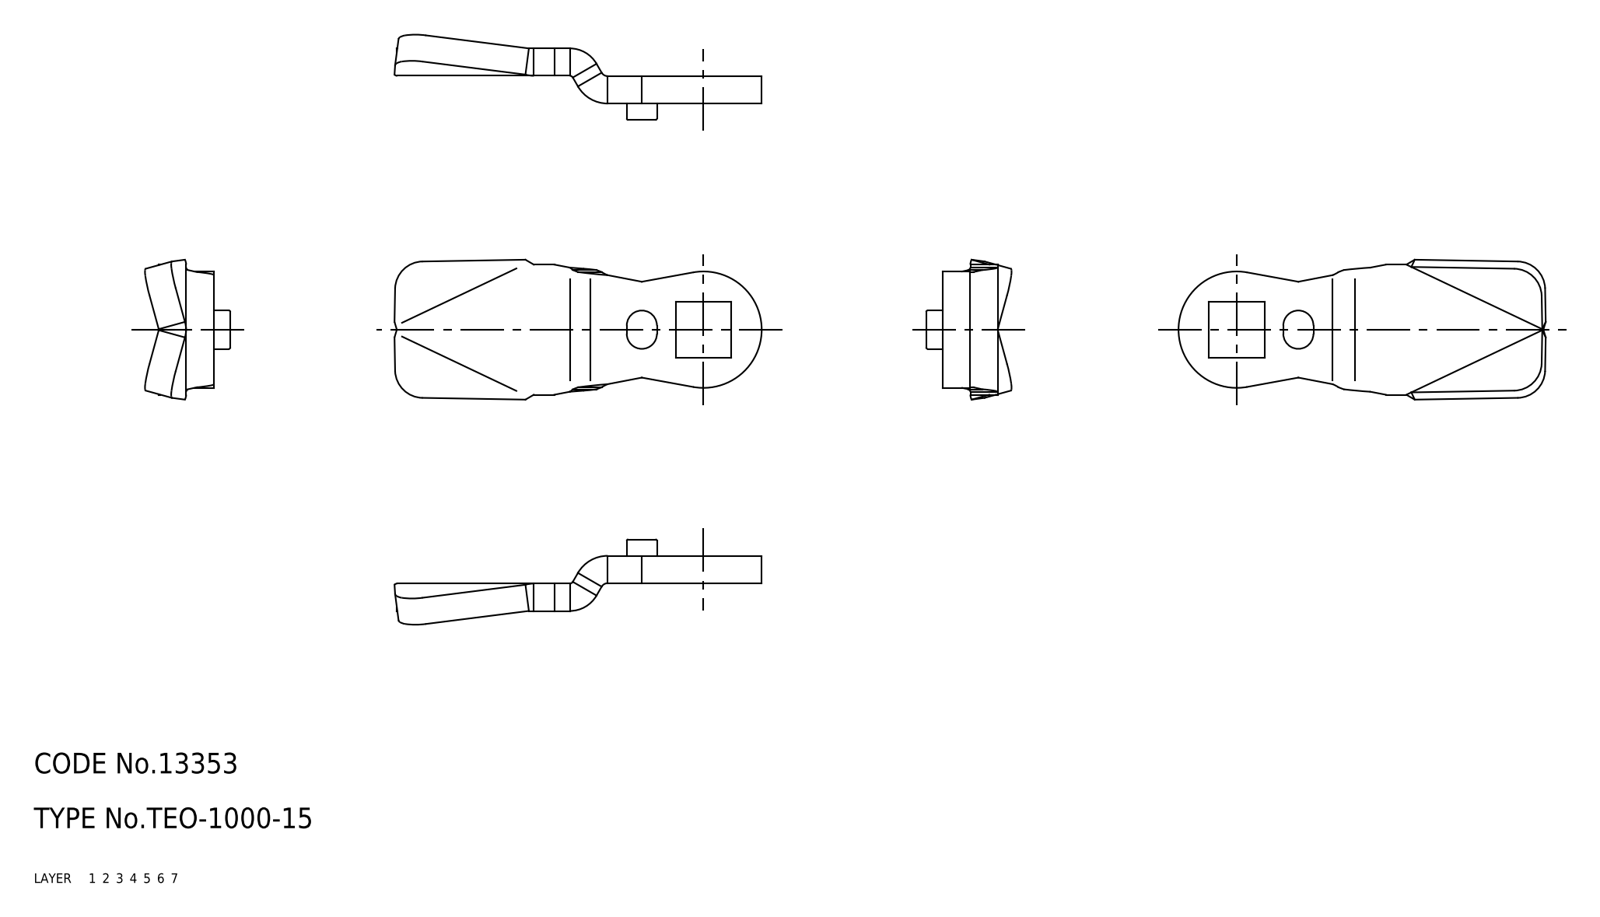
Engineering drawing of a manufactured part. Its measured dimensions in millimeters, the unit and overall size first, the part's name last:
Units: millimetres
Overall size (bounding box): 53.96 × 20.94 × 13.86
Volume: 3 651 mm³ · Surface area: 2 606 mm²
Bodies: 1 solid, 55 faces (0 planar, 0 cylindrical, 55 other)
Part name (STEP PRODUCT): cam
STEP written by: CADfix (AUTOMOTIVE_DESIGN)
